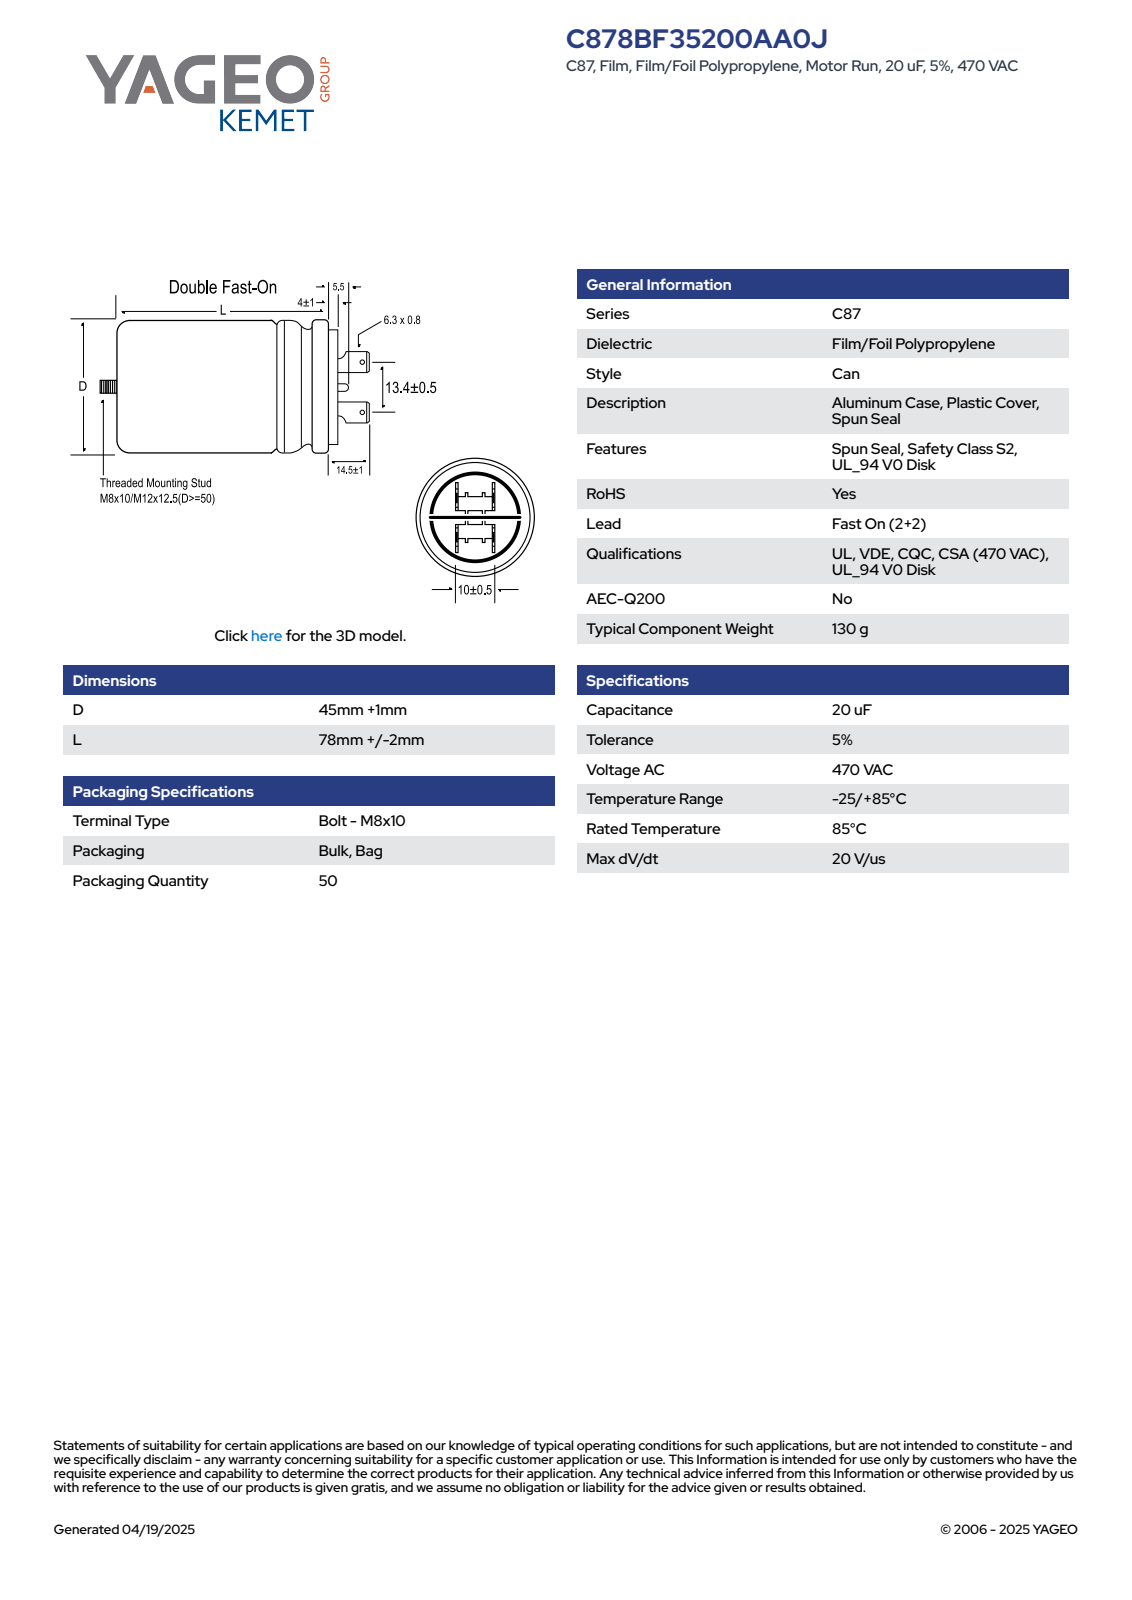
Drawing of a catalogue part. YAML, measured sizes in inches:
part_name: "CFM_C87DF_45X78_D46L80"
step_written_by: "SolidWorks 2021 (AUTOMOTIVE_DESIGN)"
units: inches
bodies: {solids: 1, faces: 153, planar: 52, cylindrical: 58, other: 43}
overall_size: [4.154, 1.811, 1.811]
volume: 8.305
surface_area: 25.85
round_holes:
  - {diameter: 0.047, count: 2}
round_bosses_or_shafts:
  - {diameter: 1.811, count: 1}
  - {diameter: 1.546, count: 1}
  - {diameter: 0.315, count: 1}
partial_cylinders:
  - {radius: 0.01, count: 9}
  - {radius: 0.157, count: 2}
  - {radius: 0.905, count: 1}
face_to_face_distances: [3.346, 2.919, 0.427, 0.031, 0.382, 3.15, 0.23, 0.197, 0.413, 0.35]
hole_center_spacings: [0.547]
